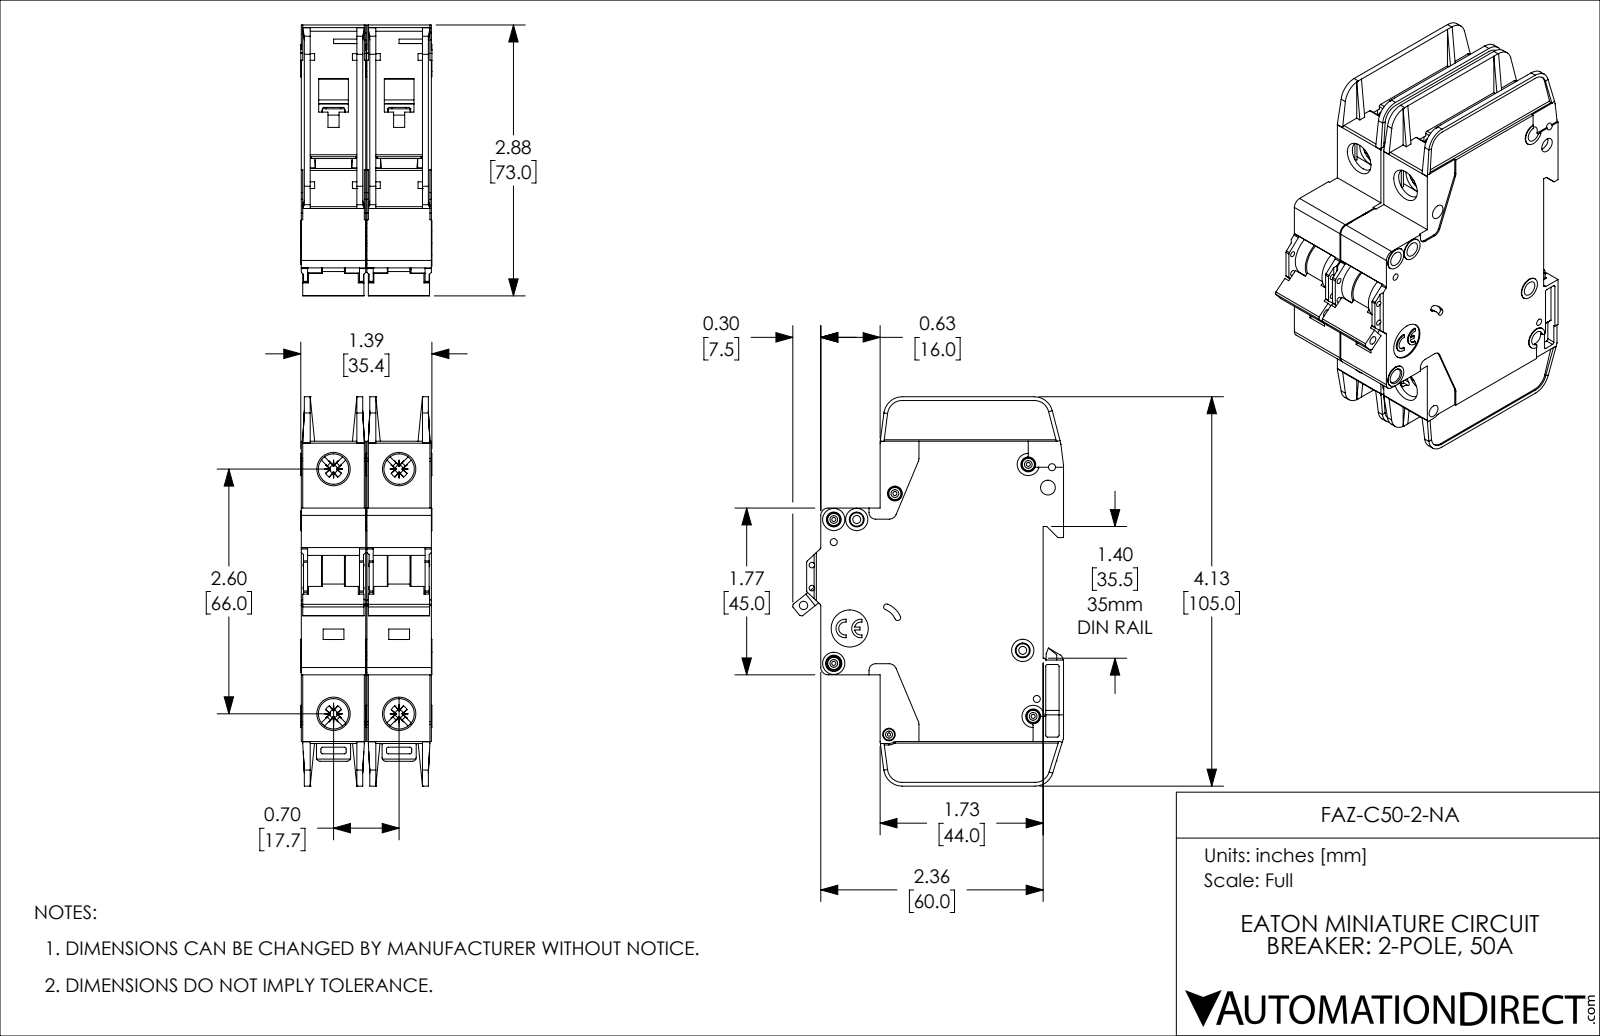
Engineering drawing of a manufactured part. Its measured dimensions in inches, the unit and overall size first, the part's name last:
Units: inches
Overall size (bounding box): 4.134 × 2.876 × 1.394
Round holes (diameter × count): ⌀0.157 ×8, ⌀0.043 ×5, ⌀0.075 ×4, ⌀0.323 ×4, ⌀0.059 ×2, ⌀0.085 ×2, ⌀0.035 ×1, ⌀0.089 ×1, ⌀0.098 ×1, ⌀0.134 ×1, ⌀0.394 ×1
Round bosses / shafts (diameter × count): ⌀0.13 ×5, ⌀0.236 ×4, ⌀0.118 ×3, ⌀0.098 ×2
Partial cylindrical surfaces — rounded edges, fillets, slot ends (radius × count): R0.02 ×57, R0.016 ×20, R0.039 ×14, R0.079 ×10, R0.043 ×8, R0.008 ×5, R0.197 ×5, R0.01 ×4
Main face-to-face distances: 0.697, 0.047, 0.685, 0.591, 0.094, 0.638, 0.543, 1.382, 0.744, 0.65
Hole centre spacings: 0.244, 0.537, 0.697, 0.87, 2.598, 2.69, 0.189, 0.199
Volume: 9.365 in³ · Surface area: 82.01 in²
Bodies: 2 solids, 2254 faces (1342 planar, 714 cylindrical, 198 other)
Part name (STEP PRODUCT): FAZ-C50-2-NA
STEP written by: SolidWorks 2019 (AUTOMOTIVE_DESIGN)
